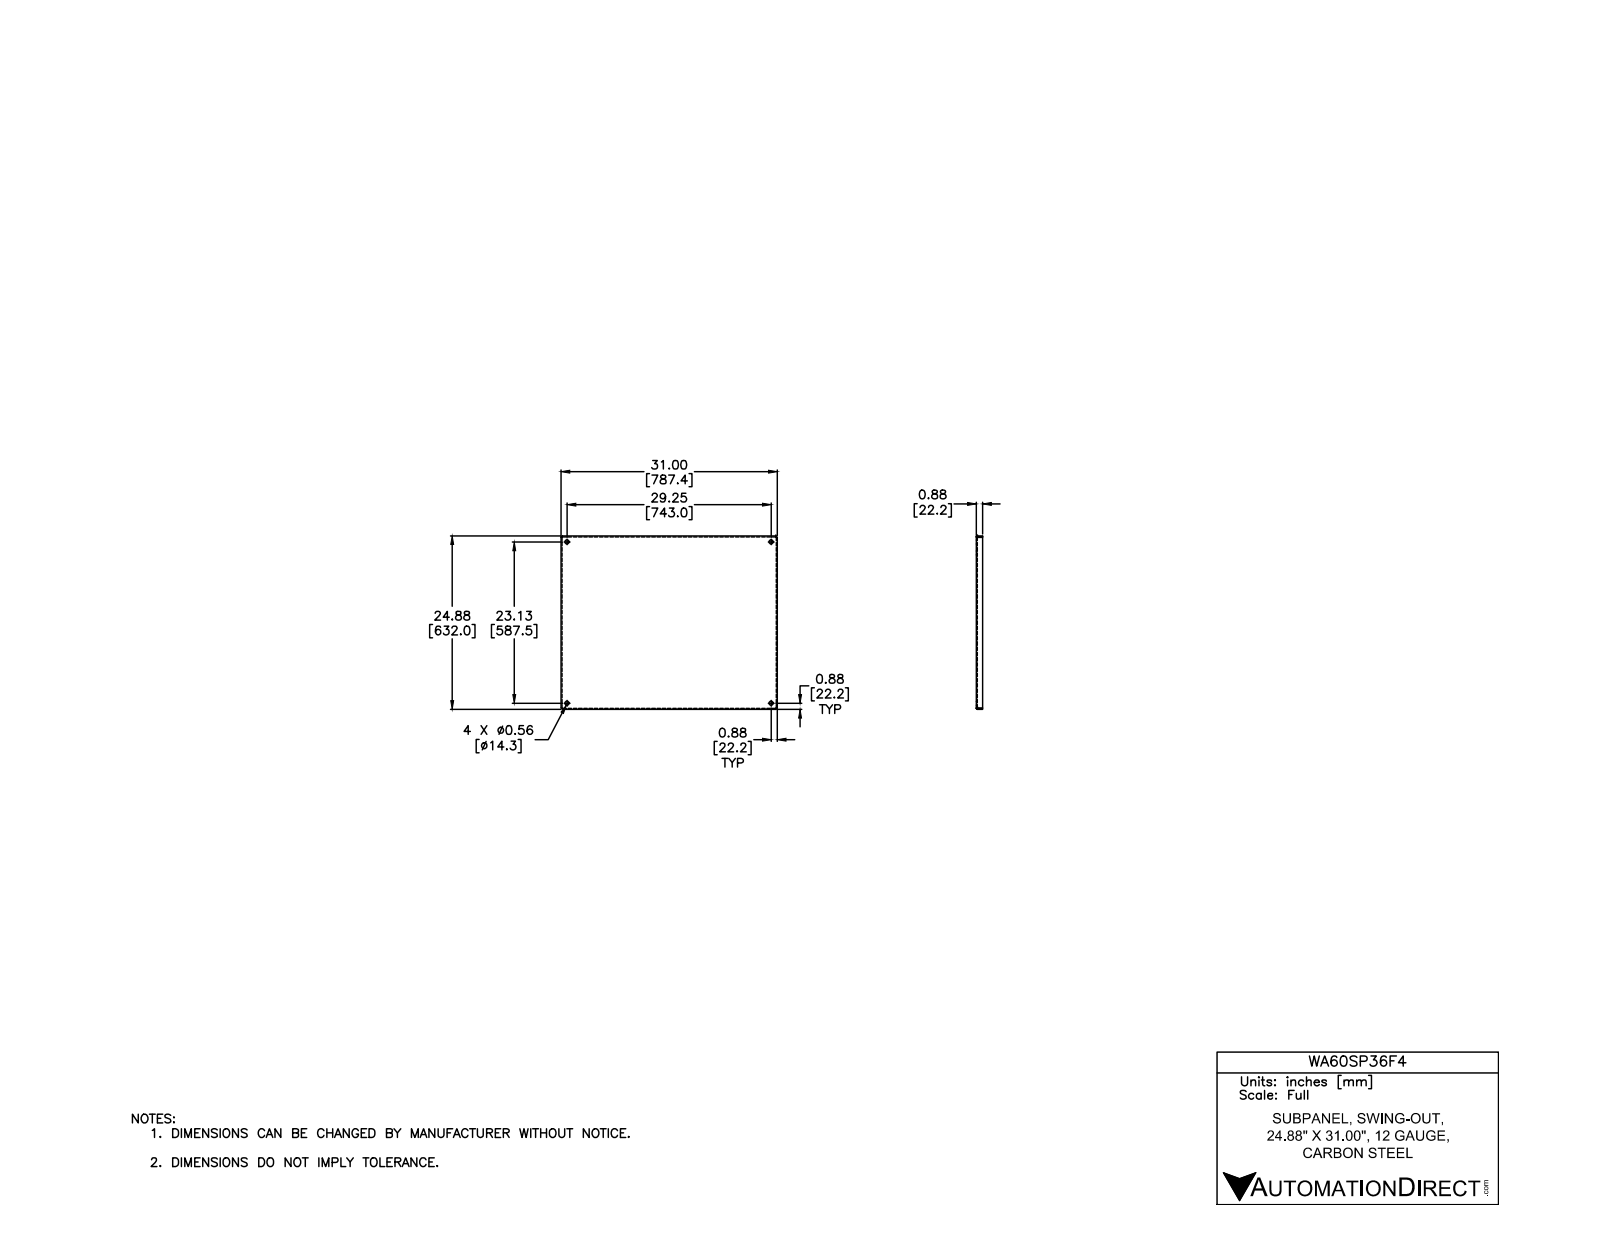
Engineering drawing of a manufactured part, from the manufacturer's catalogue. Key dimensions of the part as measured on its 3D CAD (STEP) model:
Part name (STEP PRODUCT): WA60SP24F3-WA90SP36F4
STEP written by: Autodesk Inventor 2012 (AUTOMOTIVE_DESIGN)
Units: inches
Bodies: 1 solid, 42 faces (22 planar, 12 cylindrical, 8 other)
Overall size (bounding box): 31 × 24.88 × 0.875
Volume: 79.95 in³ · Surface area: 1 717 in²
Round holes (diameter × count): ⌀0.563 ×4
Partial cylindrical surfaces — rounded edges, fillets, slot ends (radius × count): R0.031 ×4, R0.125 ×4
Main face-to-face distances: 0.094, 24.786, 30.906, 24.88, 24.693, 31, 30.813, 0.781, 0.875, 0.16
Hole centre spacings: 23.13, 29.25, 37.291
